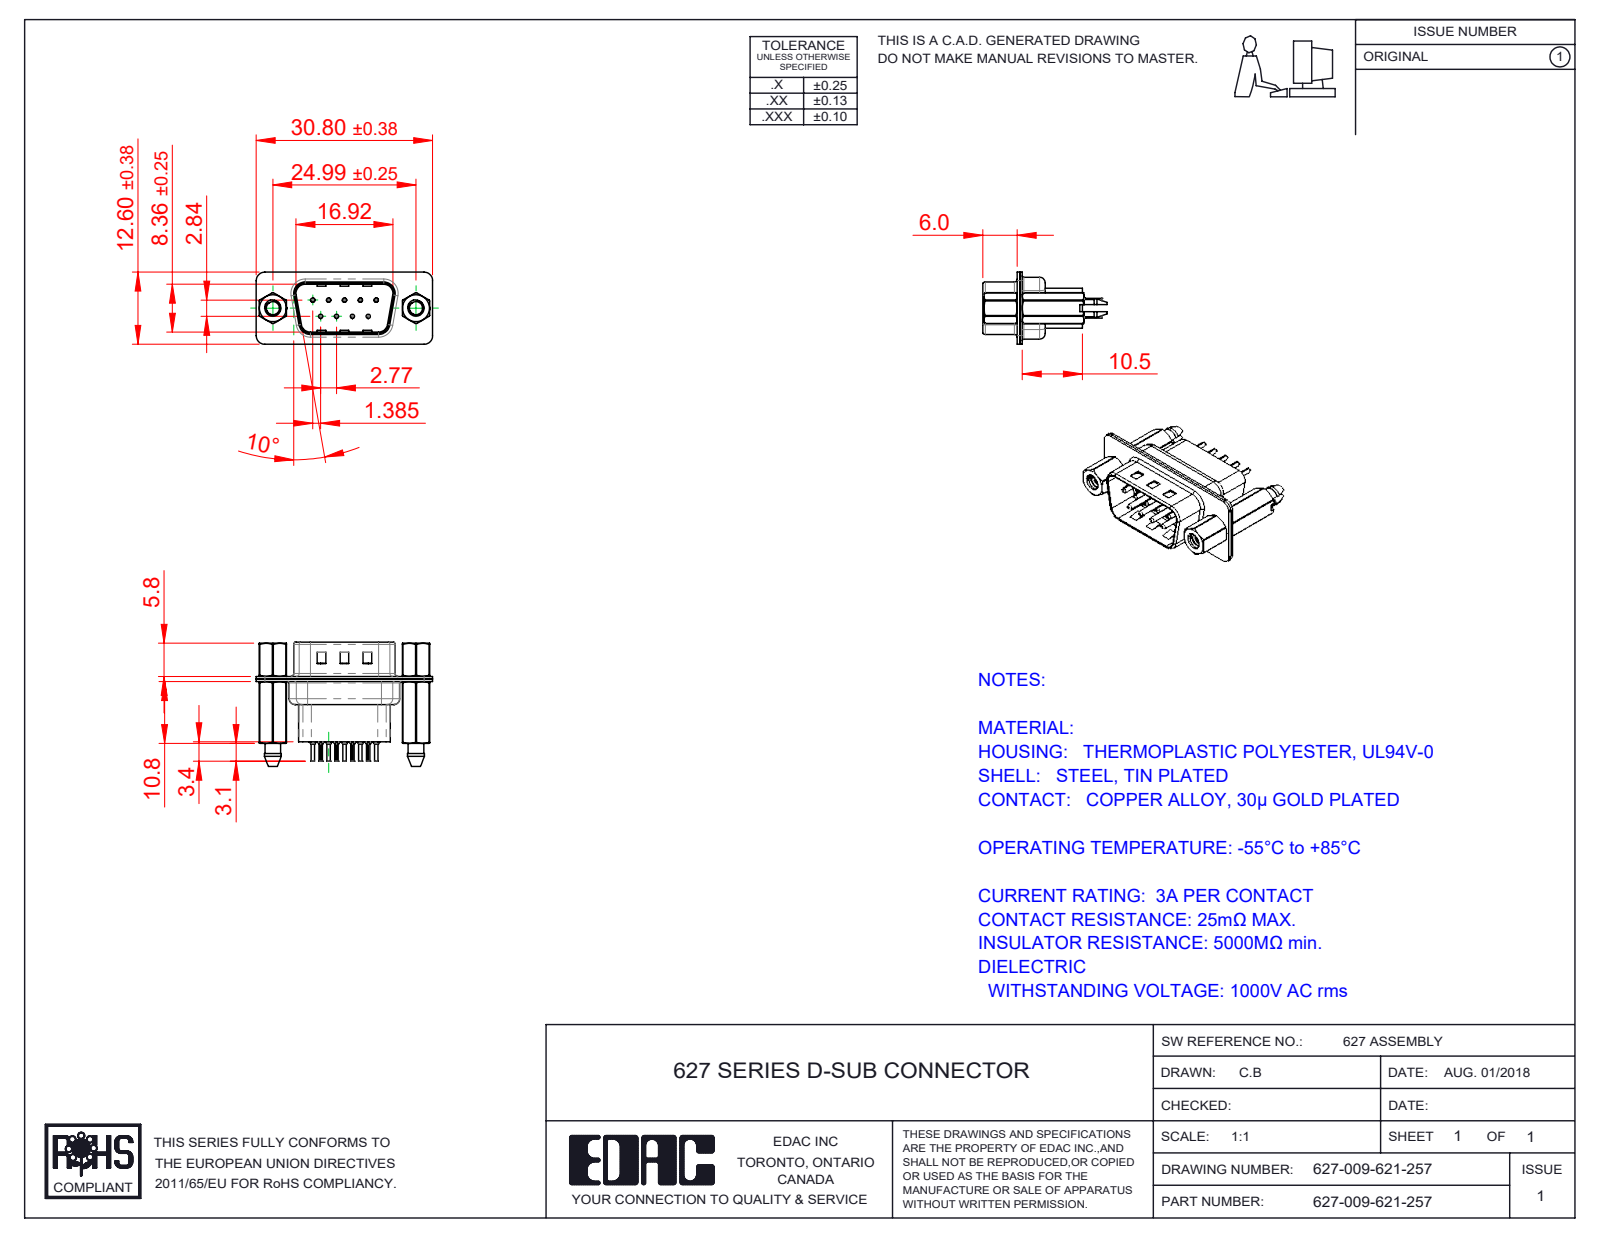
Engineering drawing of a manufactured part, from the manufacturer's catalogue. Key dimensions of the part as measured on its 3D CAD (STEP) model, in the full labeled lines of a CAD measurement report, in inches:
Part name (STEP PRODUCT): 627 4-40 Threaded Boardlock_HP; 627 Shell Front_09 Contacts; 627 Housing_09 HP; 627 Contact Row 2_21H (+4 more)
STEP written by: SolidWorks 2020 (CONFIG_CONTROL_DESIGN)
Units: inches
Bodies: 16 solids, 1426 faces (377 planar, 602 cylindrical, 447 other)
Overall size (bounding box): 1.213 × 0.854 × 0.496
Volume: 0.136 in³ · Surface area: 8.934 in²
Round holes (diameter × count): ⌀0.008 ×9, ⌀0.014 ×9, ⌀0.043 ×9, ⌀0.063 ×9, ⌀0.089 ×2, ⌀0.09 ×2, ⌀0.157 ×2, ⌀0.189 ×2
Round bosses / shafts (diameter × count): ⌀0.079 ×9, ⌀0.059 ×9, ⌀0.03 ×9, ⌀0.024 ×9, ⌀0.193 ×2, ⌀0.11 ×2
Partial cylindrical surfaces — rounded edges, fillets, slot ends (radius × count): R0.059 ×20, R0.004 ×18, R0.079 ×12, R0.063 ×10, R0.02 ×8, R0.01 ×4, R0.024 ×4, R0.026 ×4
Main face-to-face distances: 0.018, 0.016, 0.035, 0.187, 0.032, 0.377, 0.055, 0.059, 0.027, 0.302
Hole centre spacings: 0.124, 0.109, 0.218, 0.198, 0.198, 0.327, 0.294, 0.295
